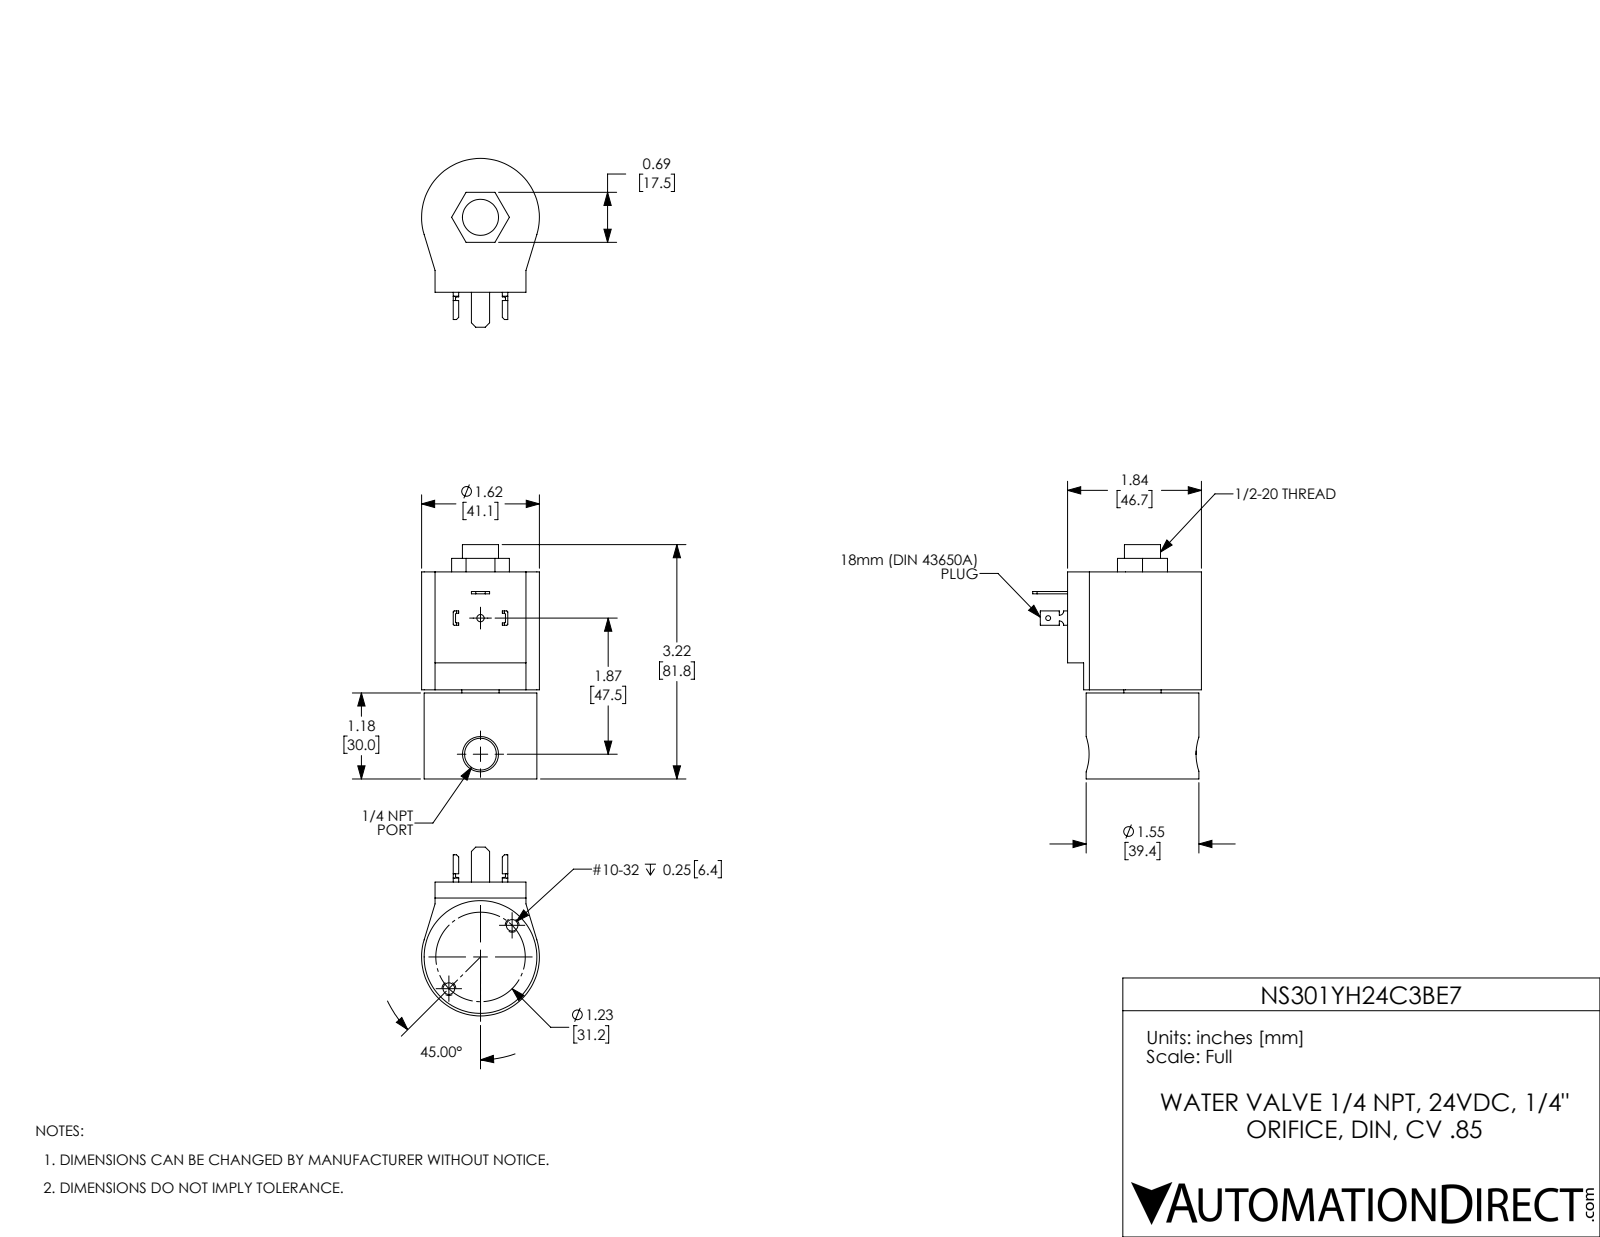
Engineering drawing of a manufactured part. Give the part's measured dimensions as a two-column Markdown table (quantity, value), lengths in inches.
| quantity | value |
| --- | --- |
| part name | NS301YH16C3BE7 |
| STEP written by | SolidWorks 2024 (CONFIG_CONTROL_DESIGN) |
| units | inches |
| bodies | 6 solids, 130 faces (73 planar, 49 cylindrical, 8 other) |
| overall size | 3.22 × 2.32 × 1.62 |
| volume | 6.042 in³ |
| surface area | 33.19 in² |
| round holes (diameter × count) | 0.159 × 2, 0.067 × 1, 0.1 × 1, 0.437 × 1, 0.496 × 1, 0.512 × 1, 1.155 × 1 |
| round bosses / shafts (diameter × count) | 1.55 × 1 |
| partial cylindrical surfaces (radius × count) | 0.015 × 8, 0.06 × 2, 0.81 × 1 |
| main face-to-face distances | 2.845, 1.182, 1.663, 1.225, 0.043, 1.62, 1.287, 0.106, 0.062, 1.558 |
| hole center spacings | 0.615, 1.23, 1.87 |
